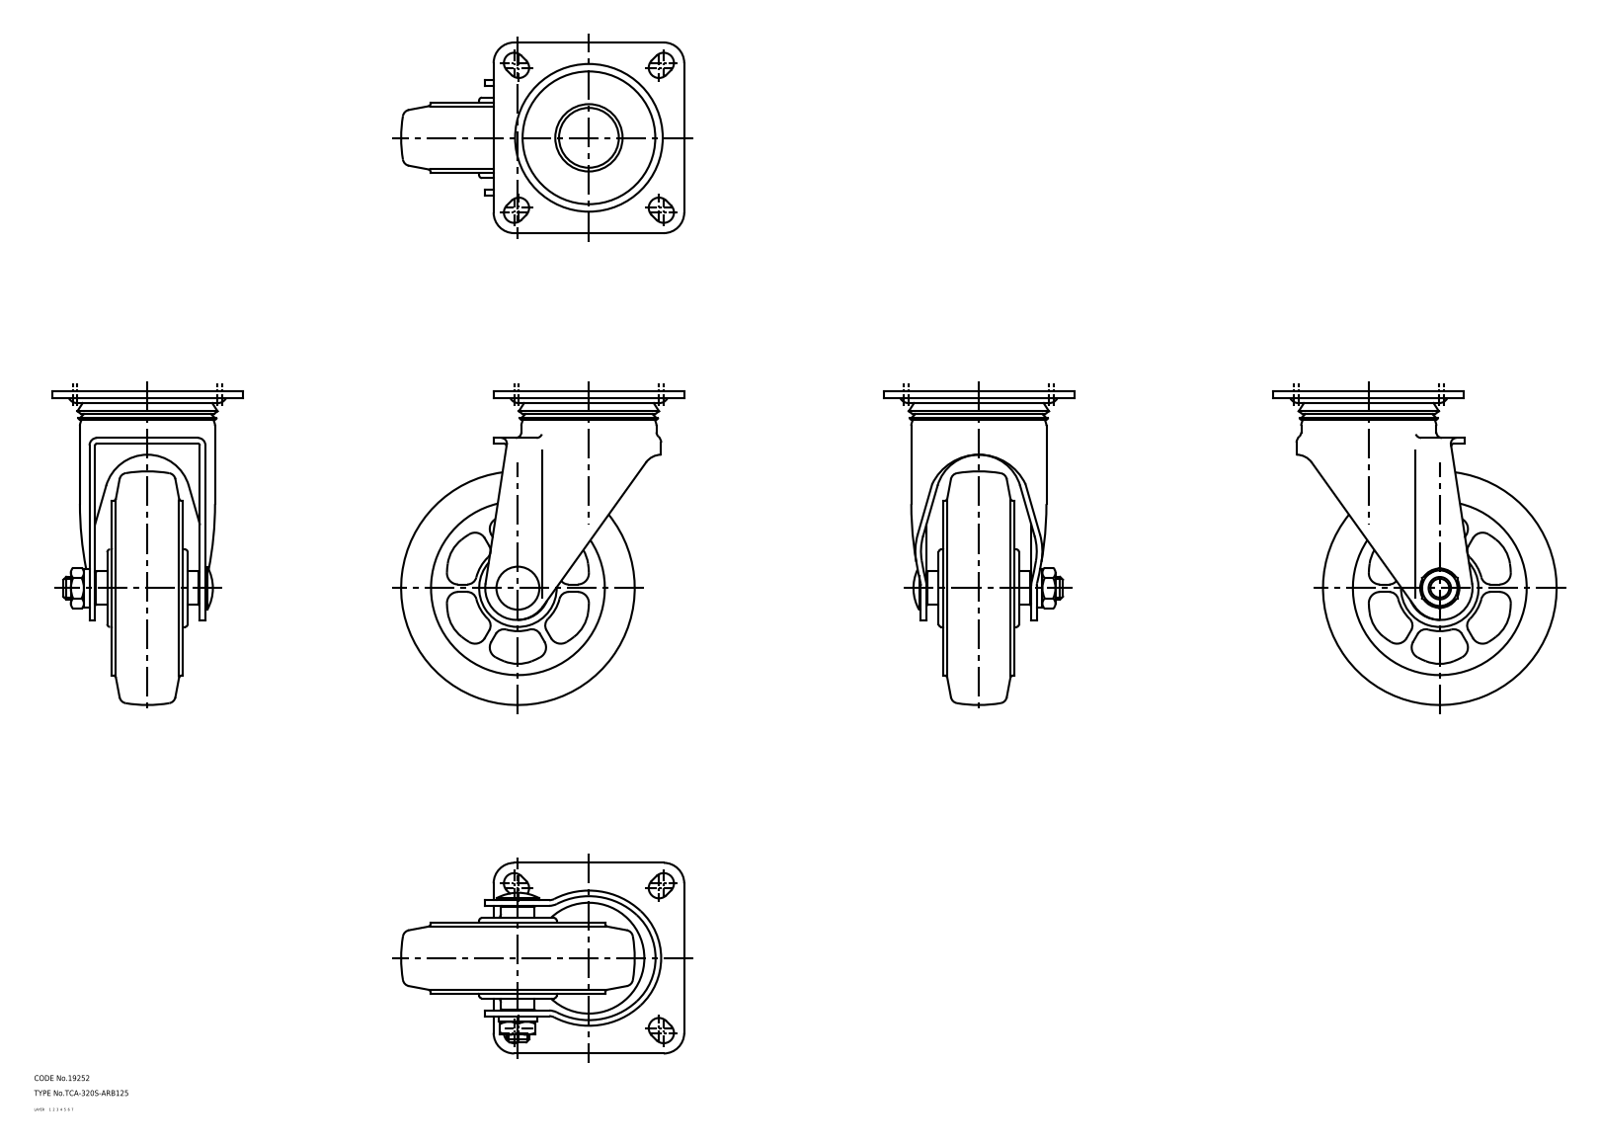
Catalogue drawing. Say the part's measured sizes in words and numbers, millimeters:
The part is named "wheel; mounting plate; main shaft; axle (+1 more)". Its 3-D file was written by "CADfix (AUTOMOTIVE_DESIGN)". It is 5 solids with 300 faces: 0 planar, 0 cylindrical and 300 other. Overall it measures 168 by 151.5 by 102 millimeters. Its volume is 493 442 cubic millimeters and its surface area 122 468 square millimeters.
